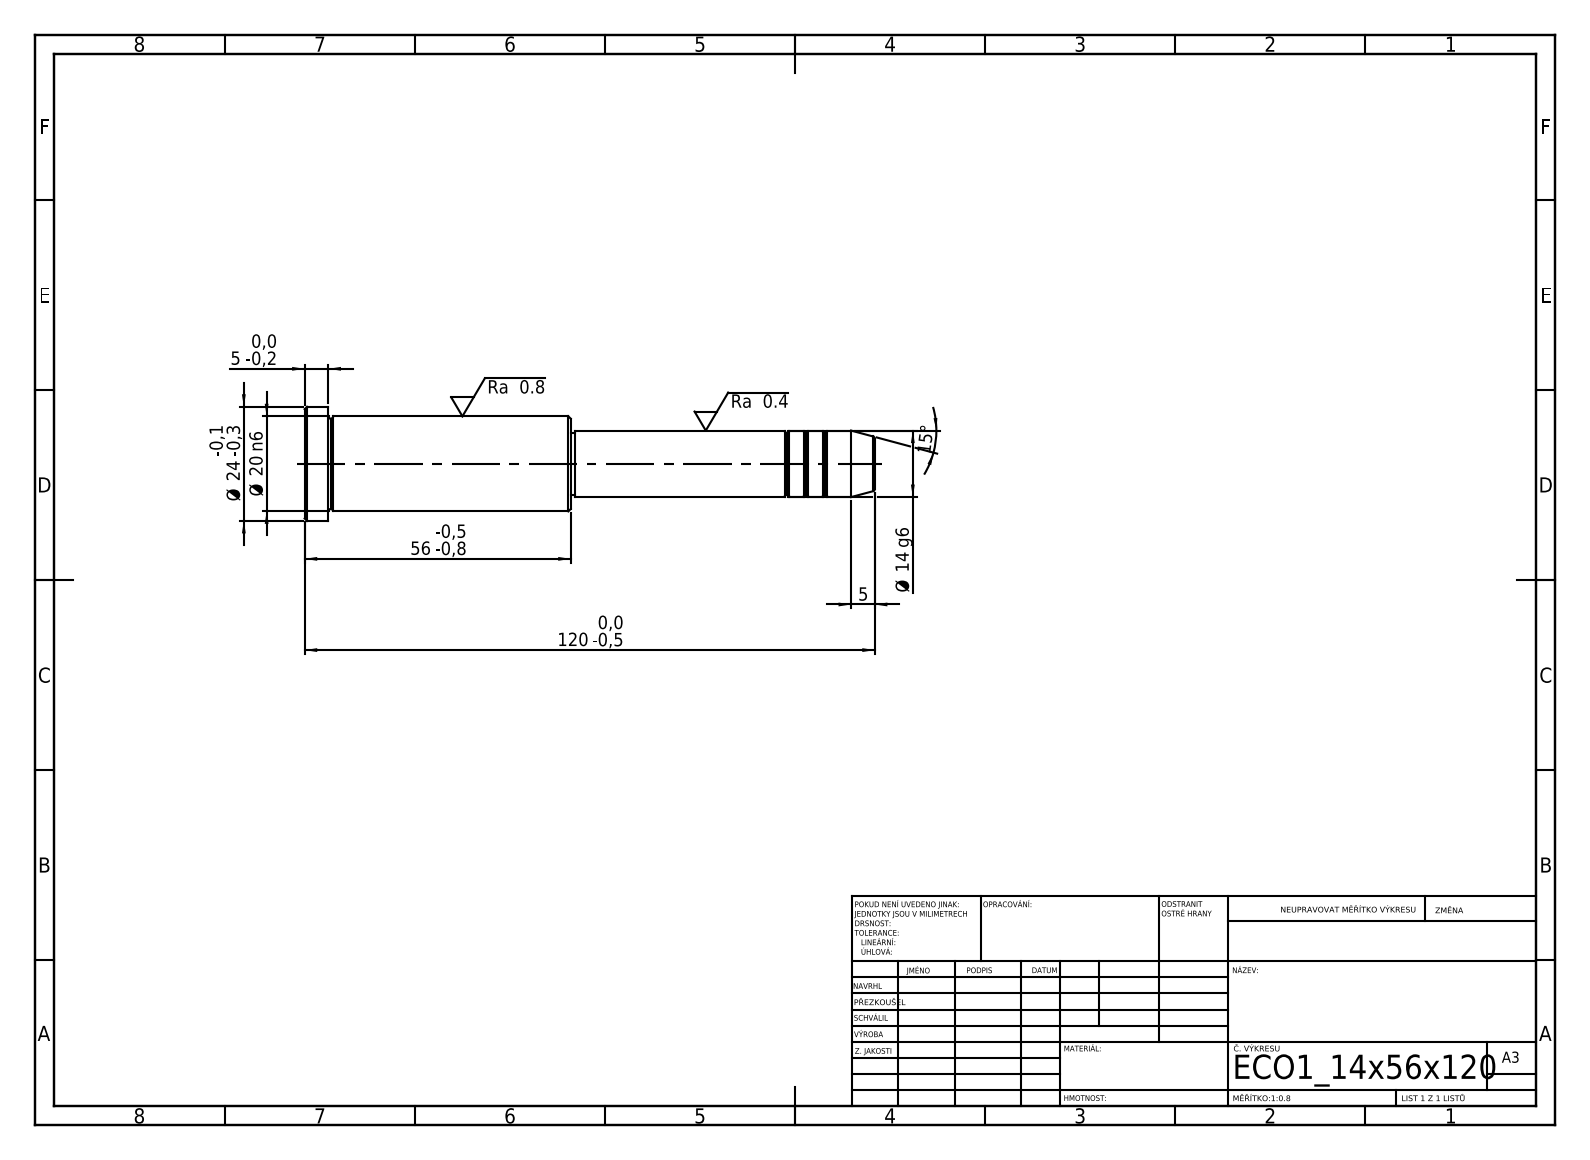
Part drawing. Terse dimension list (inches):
written by: SolidWorks 2019 (CONFIG_CONTROL_DESIGN)
unit: in
bodies: 1 solid, 43 faces (5 planar, 14 cylindrical, 24 other)
size: 4.724 × 0.945 × 0.945
volume: 1.702 in³; area: 11.36 in²
bosses: 1× ⌀0.945, 1× ⌀0.787, 1× ⌀0.551, 1× ⌀0.512
face distances: 2.205, 2.008, 0.197, 2.52, 4.528, 4.724, 2.48, 0.039, 2.047, 2.244
